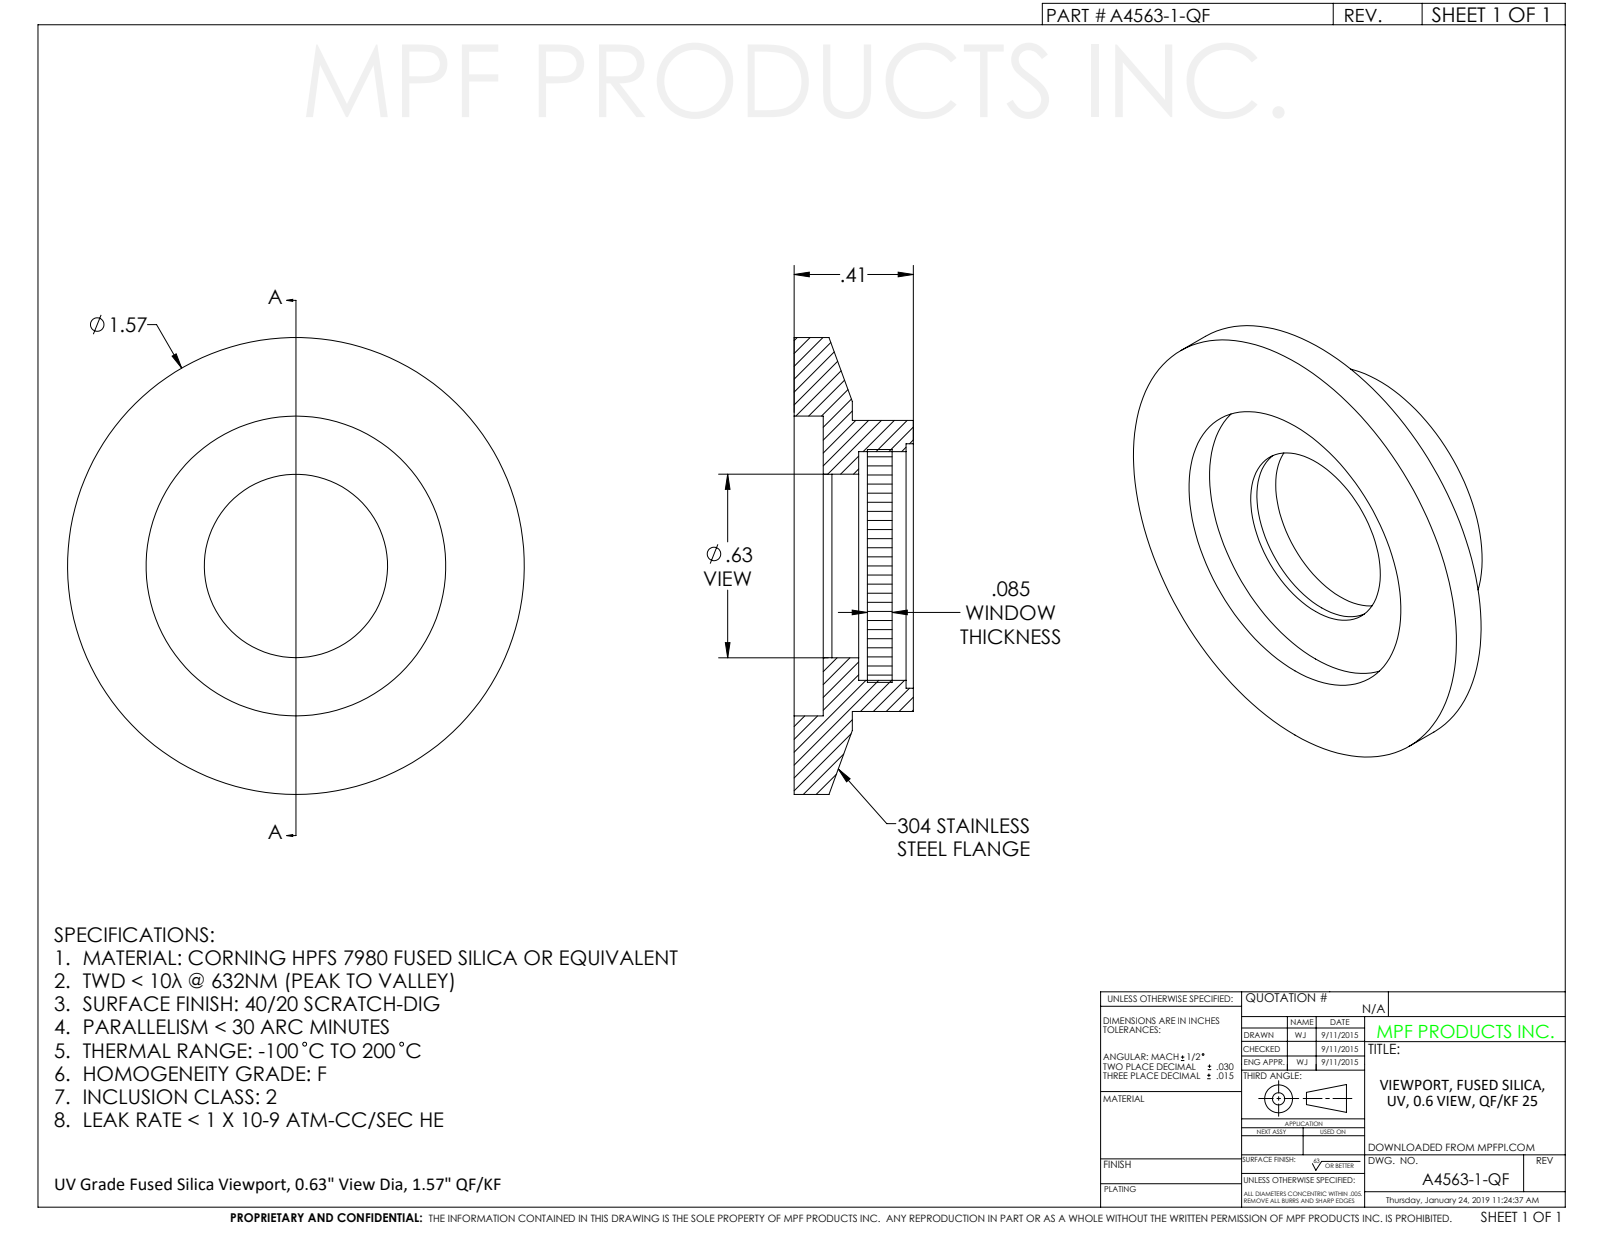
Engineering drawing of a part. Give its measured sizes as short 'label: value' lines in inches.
name: A4563-1-QF
written by: SolidWorks 2011 (CONFIG_CONTROL_DESIGN)
unit: in
bodies: 1 solid, 41 faces (11 planar, 22 cylindrical, 8 other)
size: 1.57 × 1.57 × 0.385
volume: 0.319 in³; area: 7.649 in²
holes: 1× ⌀0.63, 1× ⌀0.631, 1× ⌀0.71, 1× ⌀0.786, 1× ⌀0.84, 1× ⌀1.03
bosses: 1× ⌀1.57, 1× ⌀1, 1× ⌀0.81, 1× ⌀0.655
face distances: 0.1, 0.337, 0.237, 0.252, 0.152, 0.085, 0.385, 0.285, 0.133, 0.048
